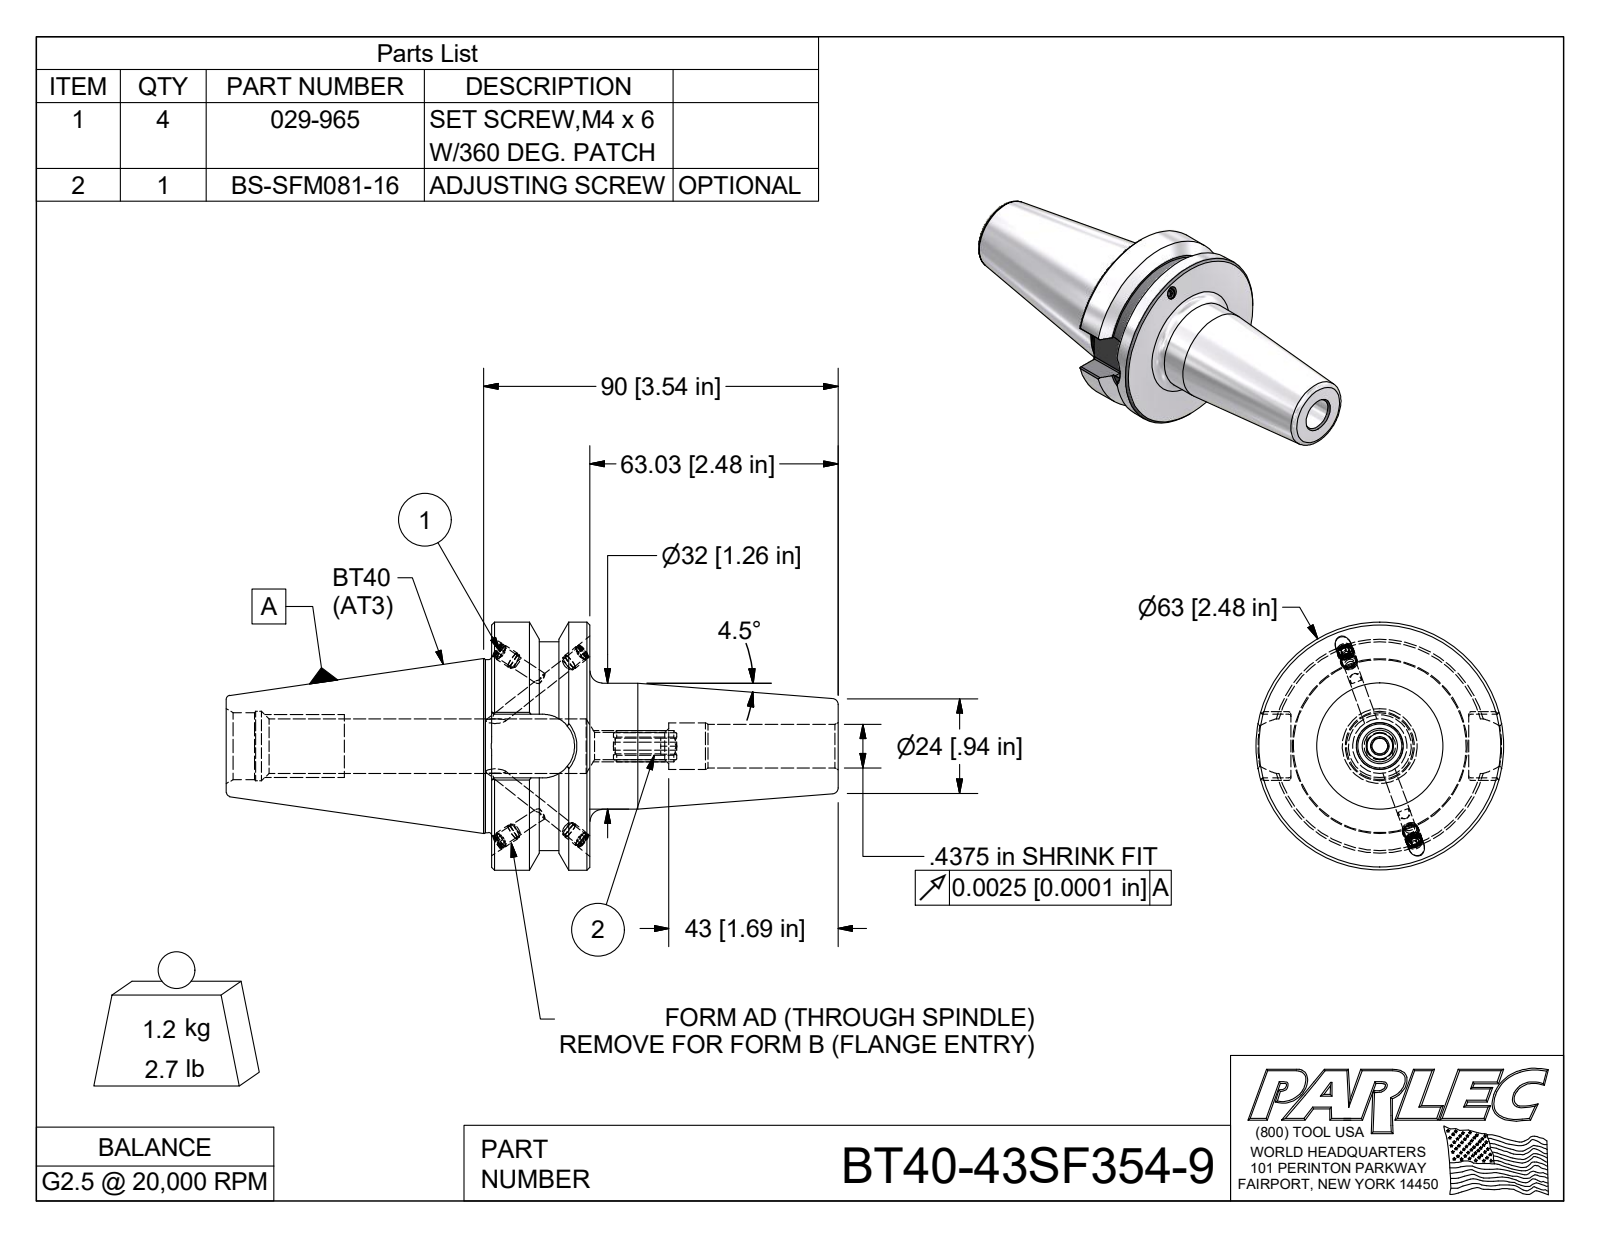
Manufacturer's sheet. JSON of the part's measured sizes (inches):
{"part_name": "BT40-43SF354-9; BT40BC-43SF354-9-1; 029-965; BS-SFM081-16", "step_written_by": "Autodesk Inventor 2009 (AUTOMOTIVE_DESIGN)", "units": "inches", "bodies": {"solids": 6, "faces": 173, "planar": 79, "cylindrical": 43, "other": 51}, "overall_size": [6.118, 2.48, 2.48], "volume_in3": 9.505, "surface_area_in2": 48.95, "round_holes": [[0.13, 4], [0.161, 4], [0.437, 1], [0.467, 1], [0.694, 1]], "round_bosses_or_shafts": [[0.165, 4], [0.157, 4], [2.48, 1], [2.087, 1], [1.75, 1], [1.73, 1], [1.26, 1]], "partial_cylinders_radius": [[0.02, 8], [0.157, 1], [0.319, 1]], "face_to_face_distances": [0.984, 1.78, 3.465, 2.481, 2.653, 3.637, 6.119, 0.637, 0.762, 1.018]}
